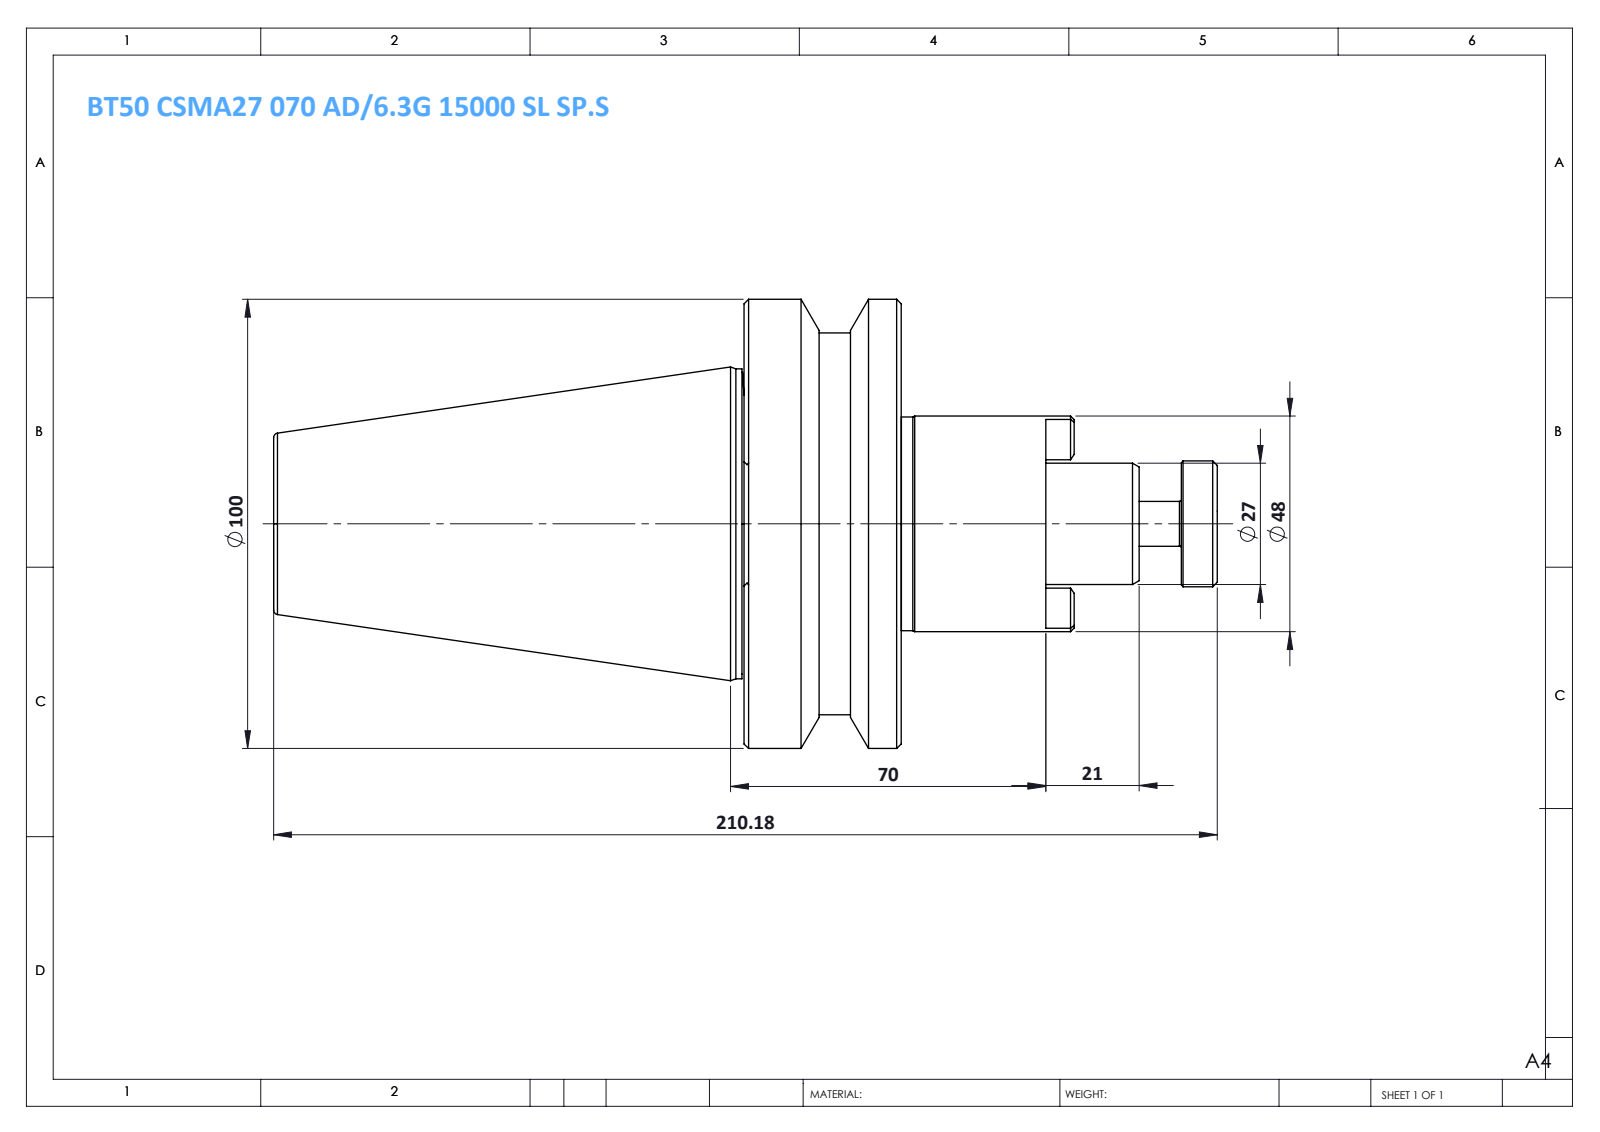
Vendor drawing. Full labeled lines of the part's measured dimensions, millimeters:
Part name (STEP PRODUCT): BT50 CSMA27 070 AD-6.3G 15000 SL SP.S
STEP written by: SolidWorks 2014 (CONFIG_CONTROL_DESIGN)
Units: millimetres
Bodies: 1 solid, 75 faces (19 planar, 20 cylindrical, 36 other)
Overall size (bounding box): 210.18 × 100 × 100
Volume: 586 977 mm³ · Surface area: 53 445 mm²
Round bosses / shafts (diameter × count): ⌀100 ×1, ⌀85 ×1, ⌀69 ×1, ⌀48 ×1, ⌀47.6 ×1, ⌀28 ×1, ⌀27 ×1, ⌀10 ×1
Partial cylindrical surfaces — rounded edges, fillets, slot ends (radius × count): R15.5 ×1
Main face-to-face distances: 35, 139.8, 104.8, 32.2, 67.2, 172, 38.18, 70.38, 105.38, 210.18
